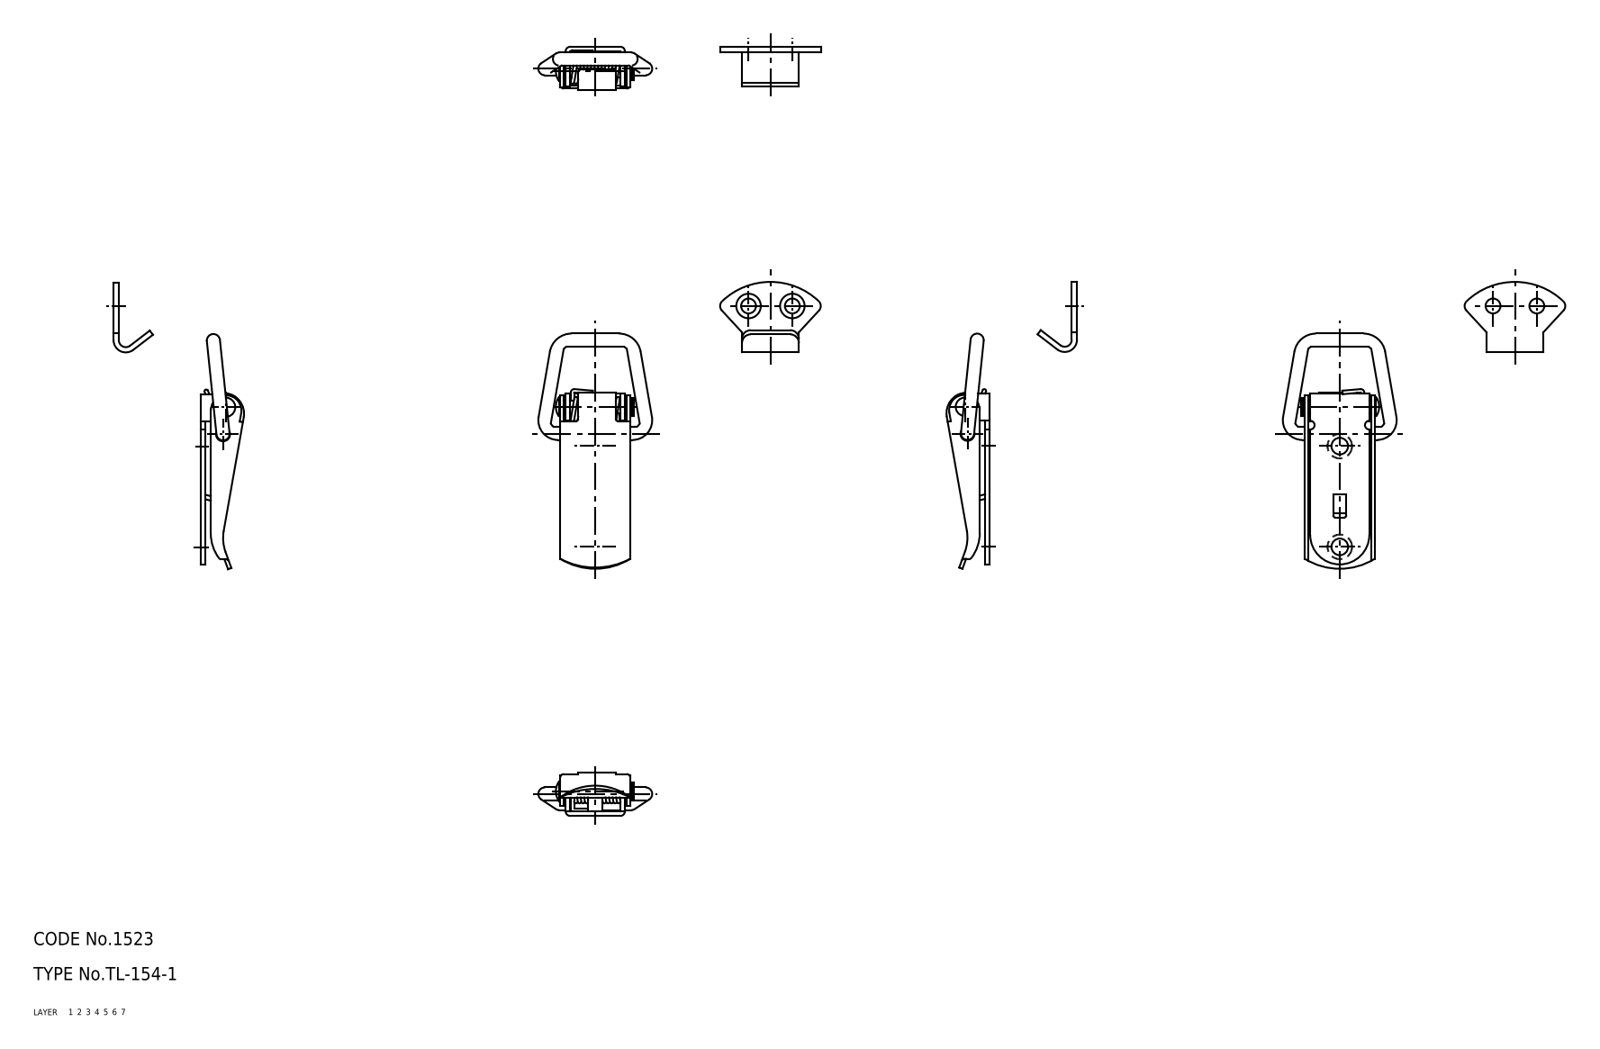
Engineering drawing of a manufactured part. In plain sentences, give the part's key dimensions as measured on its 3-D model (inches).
The part is named "spring; shaft; lever; keeper (+3 more)". Its 3-D file was written by "CADfix (AUTOMOTIVE_DESIGN)". It is 6 solids with 169 faces: 0 planar, 0 cylindrical and 169 other. Overall it measures 2.579 by 1.025 by 0.386 inches. Its volume is 0.146 cubic inches and its surface area 8.238 square inches.
